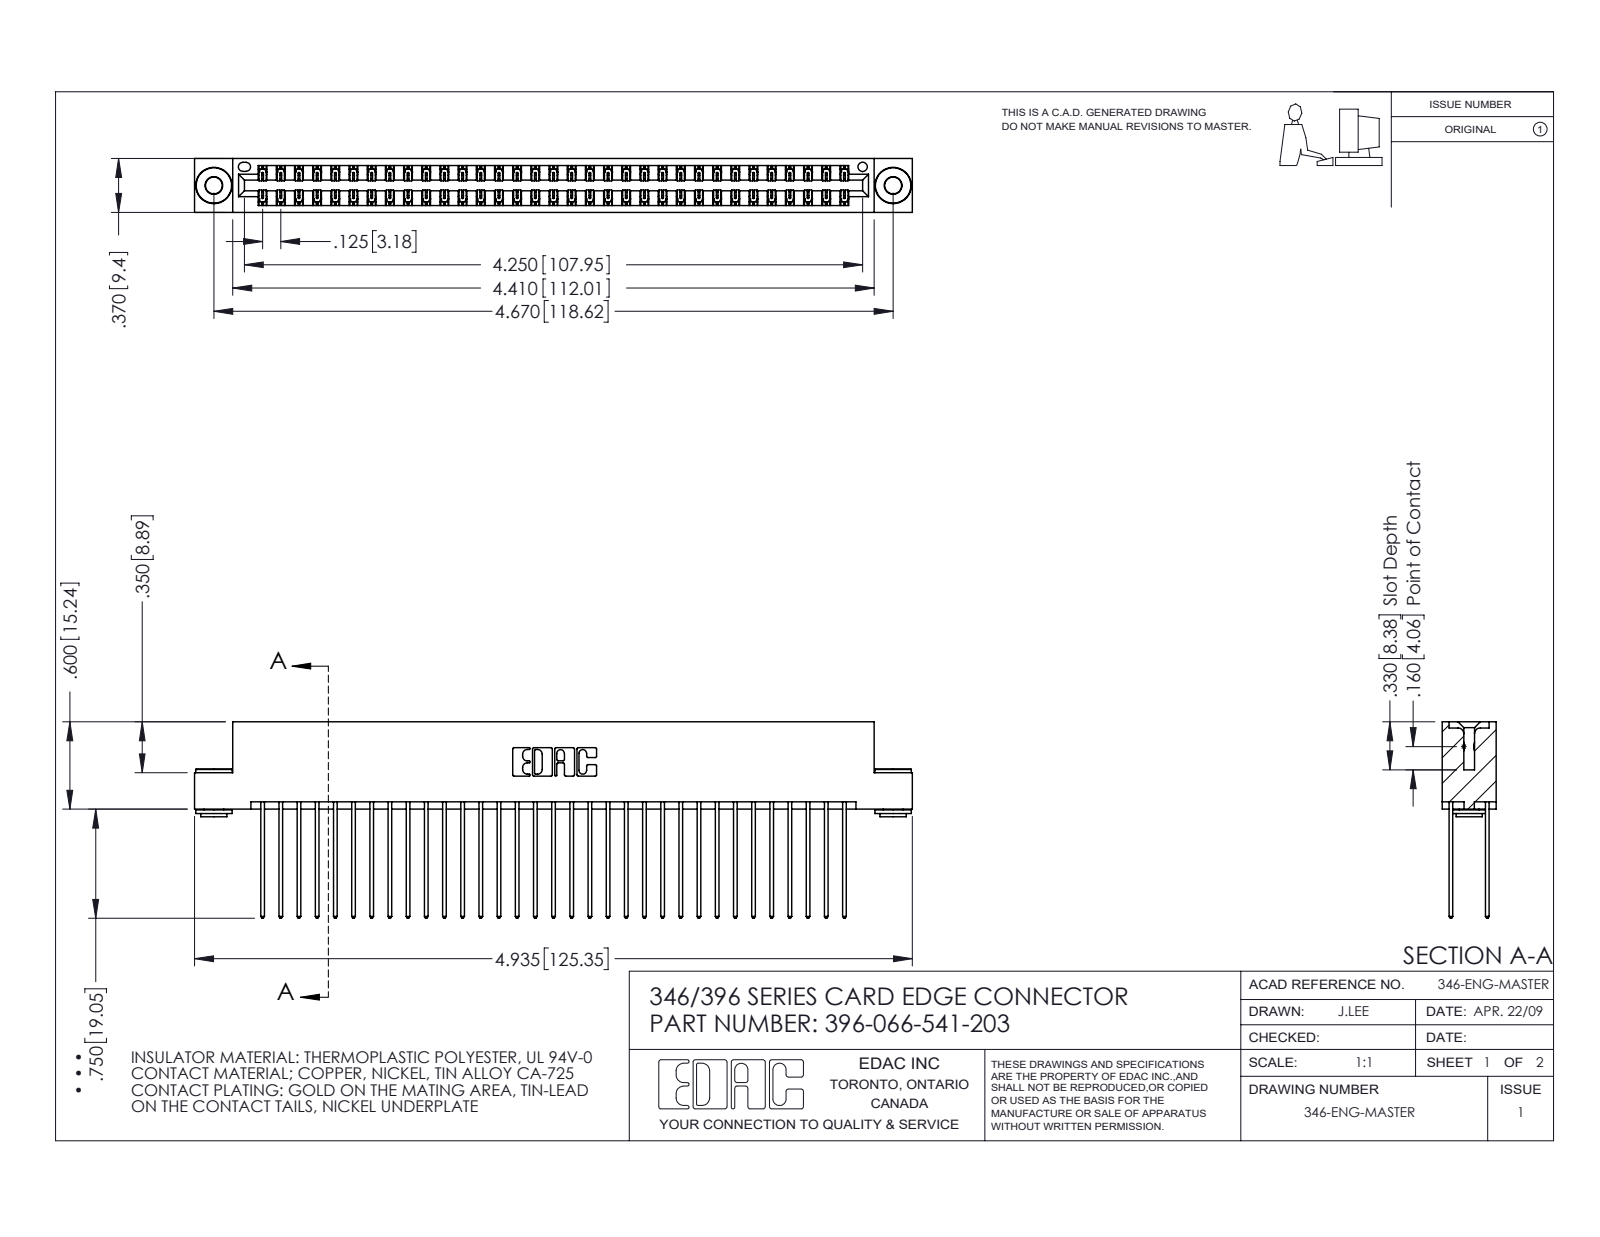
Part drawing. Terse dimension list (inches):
name: 345-292-001_345-293-141; 346 Part_Flush Mounting Lugs - 0.156 Dia-TH; 345-250-002_345-250-002-102; 396-066-541-203
written by: SolidWorks 2016 (CONFIG_CONTROL_DESIGN)
unit: in
bodies: 69 solids, 3592 faces (2396 planar, 1188 cylindrical, 8 other)
size: 4.935 × 1.35 × 0.37
volume: 0.766 in³; area: 29.67 in²
holes: 2× ⌀0.116, 2× ⌀0.156, 1× ⌀0.064
bosses: 2× ⌀0.25, 2× ⌀0.18, 2× ⌀0.136
rounds: 99× R0.006, 66× R0.01, 22× R0.01, 6× R0.007, 6× R0.031, 3× R0.026, 2× R0.014, 2× R0.022
face distances: 0.048, 0.322, 0.25, 0.025, 0.072, 0.298, 0.37, 0.275, 0.225, 0.148
hole spacings: 0.246, 4.462, 4.67
